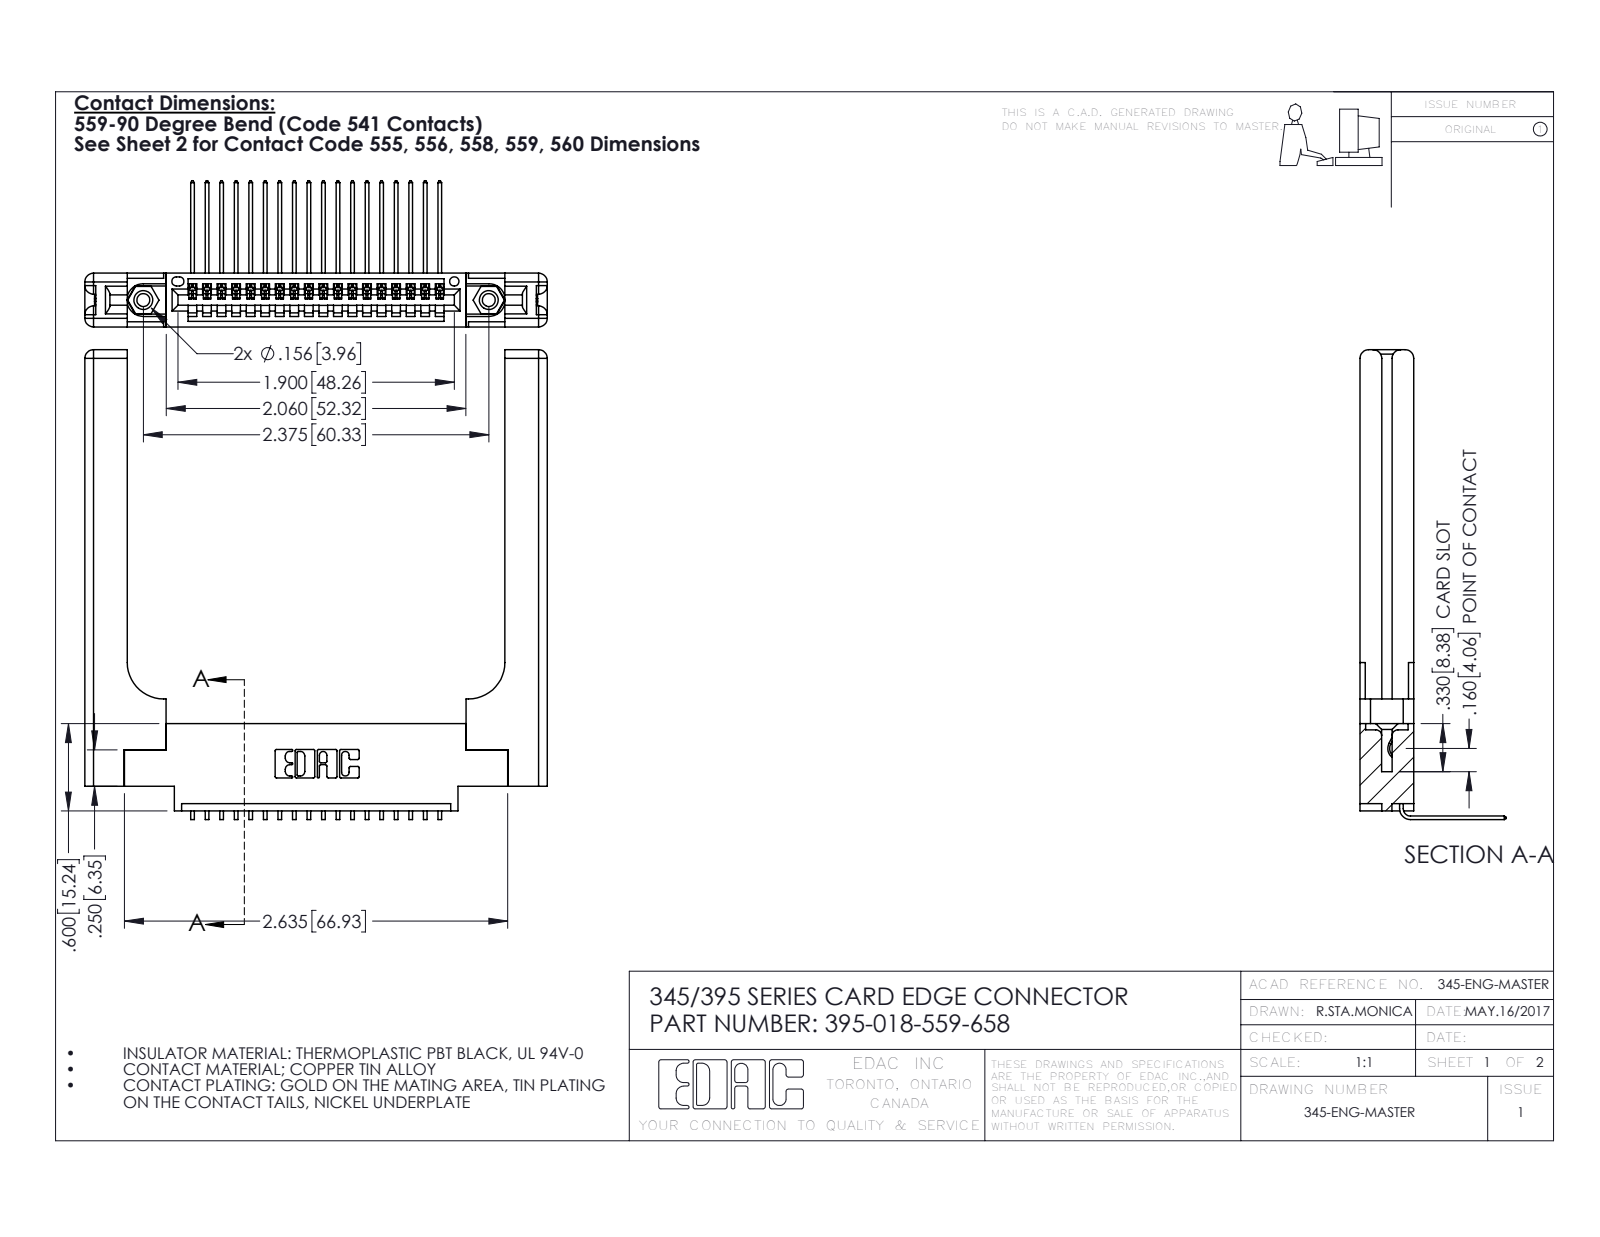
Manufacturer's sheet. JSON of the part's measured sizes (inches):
{"part_name": "395-018-559-658; 345-220-058_345-220-058; 345-250-001_345-250-001-102; 345 Part_0.170 Offset - 0.156 Dia-TH (+1 more)", "step_written_by": "SolidWorks 2016 (CONFIG_CONTROL_DESIGN)", "units": "inches", "bodies": {"solids": 23, "faces": 1466, "planar": 988, "cylindrical": 418, "other": 60}, "overall_size": [3.229, 3.179, 1.005], "volume_in3": 0.972, "surface_area_in2": 23.74, "round_holes": [[0.089, 2], [0.125, 2], [0.156, 2], [0.064, 1]], "round_bosses_or_shafts": [[0.155, 2]], "partial_cylinders_radius": [[0.006, 36], [0.01, 22], [0.06, 16], [0.007, 6], [0.031, 6], [0.026, 3], [0.03, 2], [0.031, 2]], "face_to_face_distances": [0.37, 0.072, 0.298, 0.148, 0.15, 0.077, 0.22, 0.123, 0.098, 0.272], "hole_center_spacings": [0.27, 2.141, 2.375]}
